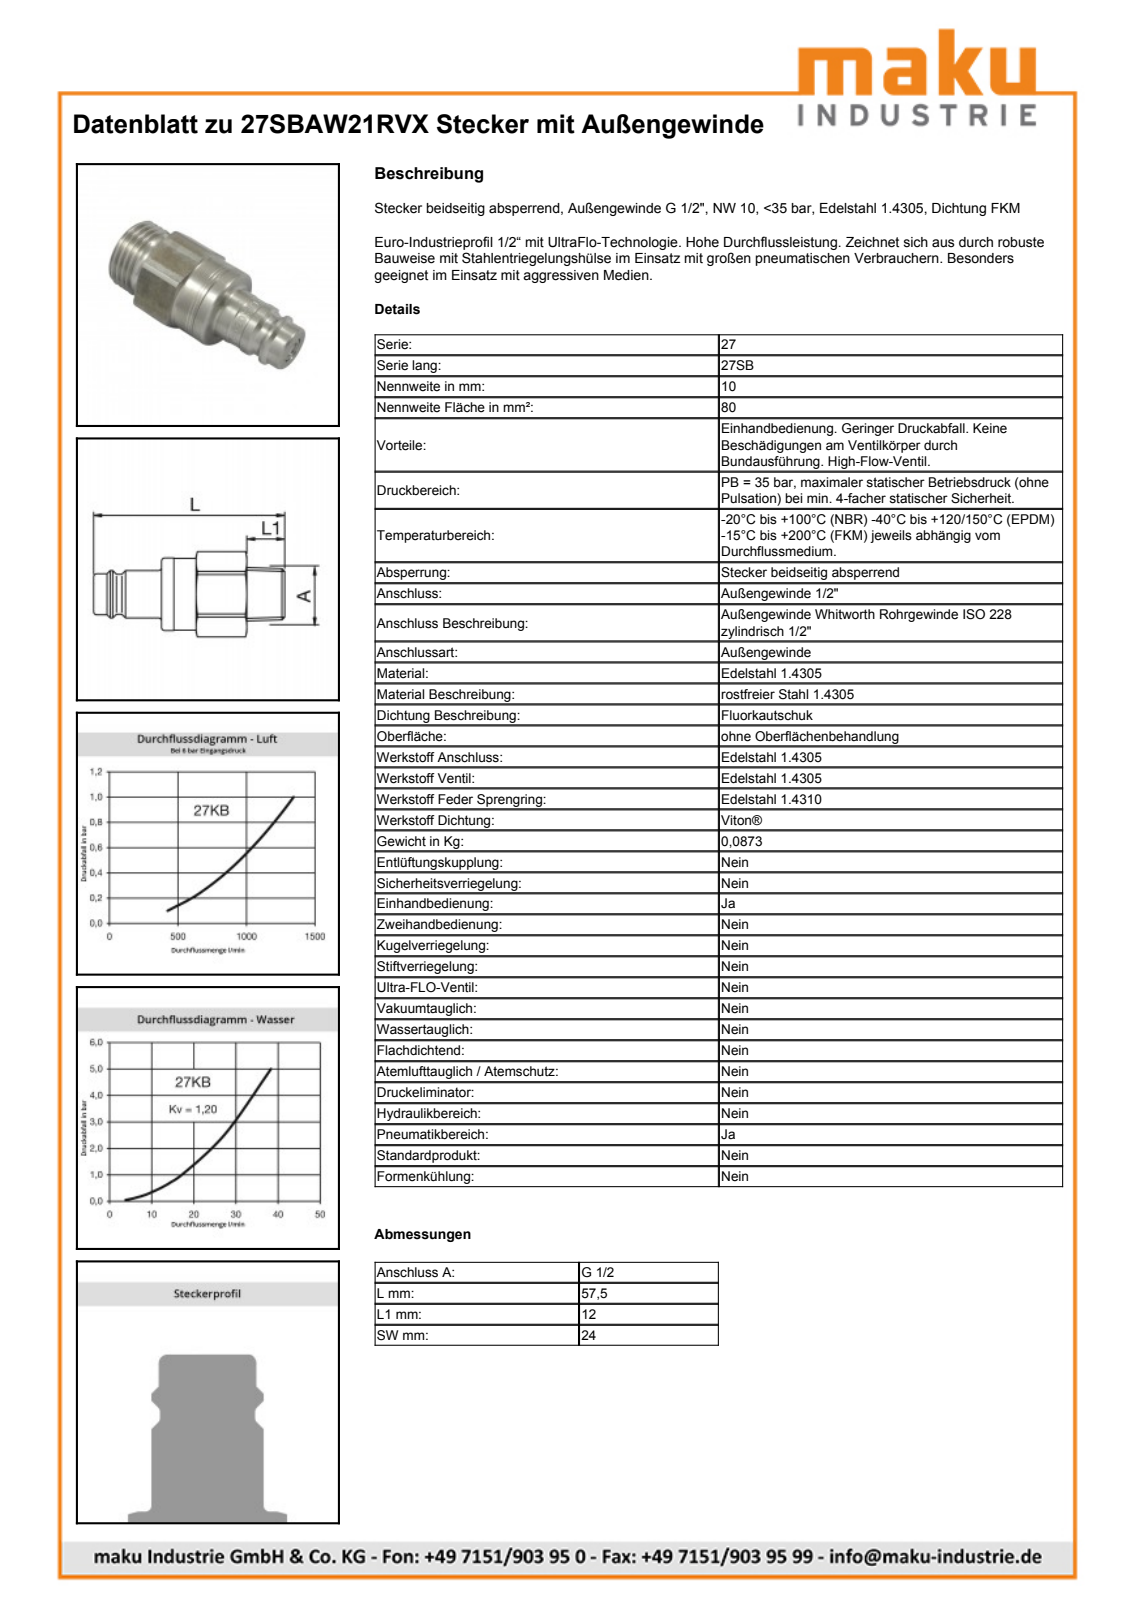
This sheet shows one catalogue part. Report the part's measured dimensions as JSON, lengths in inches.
{"part_name": "D104119", "step_written_by": "Autodesk Inventor 2011 (AUTOMOTIVE_DESIGN)", "units": "inches", "bodies": {"solids": 1, "faces": 56, "planar": 13, "cylindrical": 16, "other": 27}, "overall_size": [2.26, 1.061, 1.002], "volume_in3": 1.111, "surface_area_in2": 7.394, "round_holes": [[0.748, 1], [0.799, 1]], "round_bosses_or_shafts": [[0.906, 1], [0.898, 1], [0.825, 1], [0.728, 1], [0.591, 1], [0.512, 1], [0.498, 1]], "partial_cylinders_radius": [[0.533, 1]], "face_to_face_distances": [0.945, 0.946, 1.413, 0.941, 0.472, 0.846, 1.787, 2.26, 1, 0.154]}
